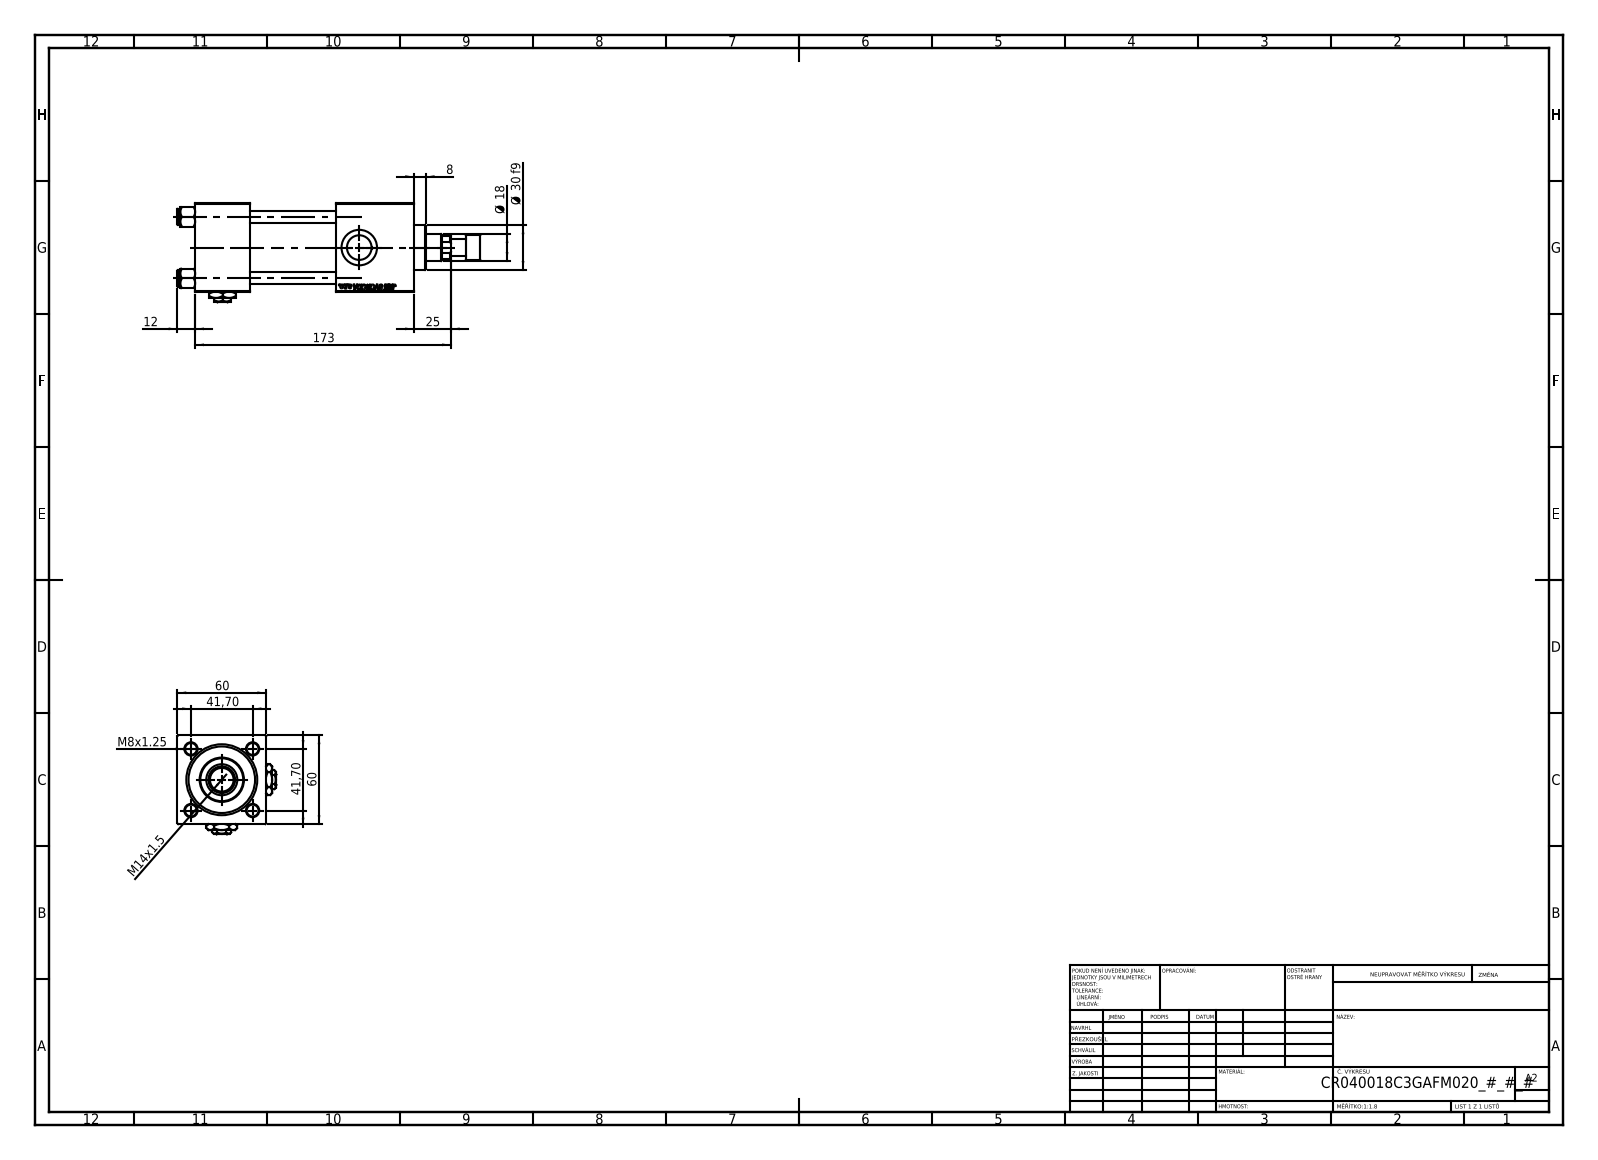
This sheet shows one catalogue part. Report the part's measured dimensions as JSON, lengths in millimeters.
{"part_name": "V215CR_ROD_END_F; V215CR_C_Body; NUT_M5_C; V215CR_VCP_C (+3 more)", "step_written_by": "SolidWorks 2019 (CONFIG_CONTROL_DESIGN)", "units": "millimeters", "bodies": {"solids": 14, "faces": 1261, "planar": 577, "cylindrical": 102, "other": 582}, "overall_size": [205, 67, 67], "volume_mm3": 402055, "surface_area_mm2": 109646, "round_holes": [[8, 4], [7, 2], [16.66, 2], [24, 2], [8.5, 1], [18, 1], [21, 1], [31, 1], [40, 1], [45, 1]], "round_bosses_or_shafts": [[11, 5], [46, 1], [30, 1], [17, 1]], "face_to_face_distances": [60, 37, 53, 148, 111, 58, 95, 119.3, 82.3, 24.3], "hole_center_spacings": [29.49, 41.7, 58.97]}
